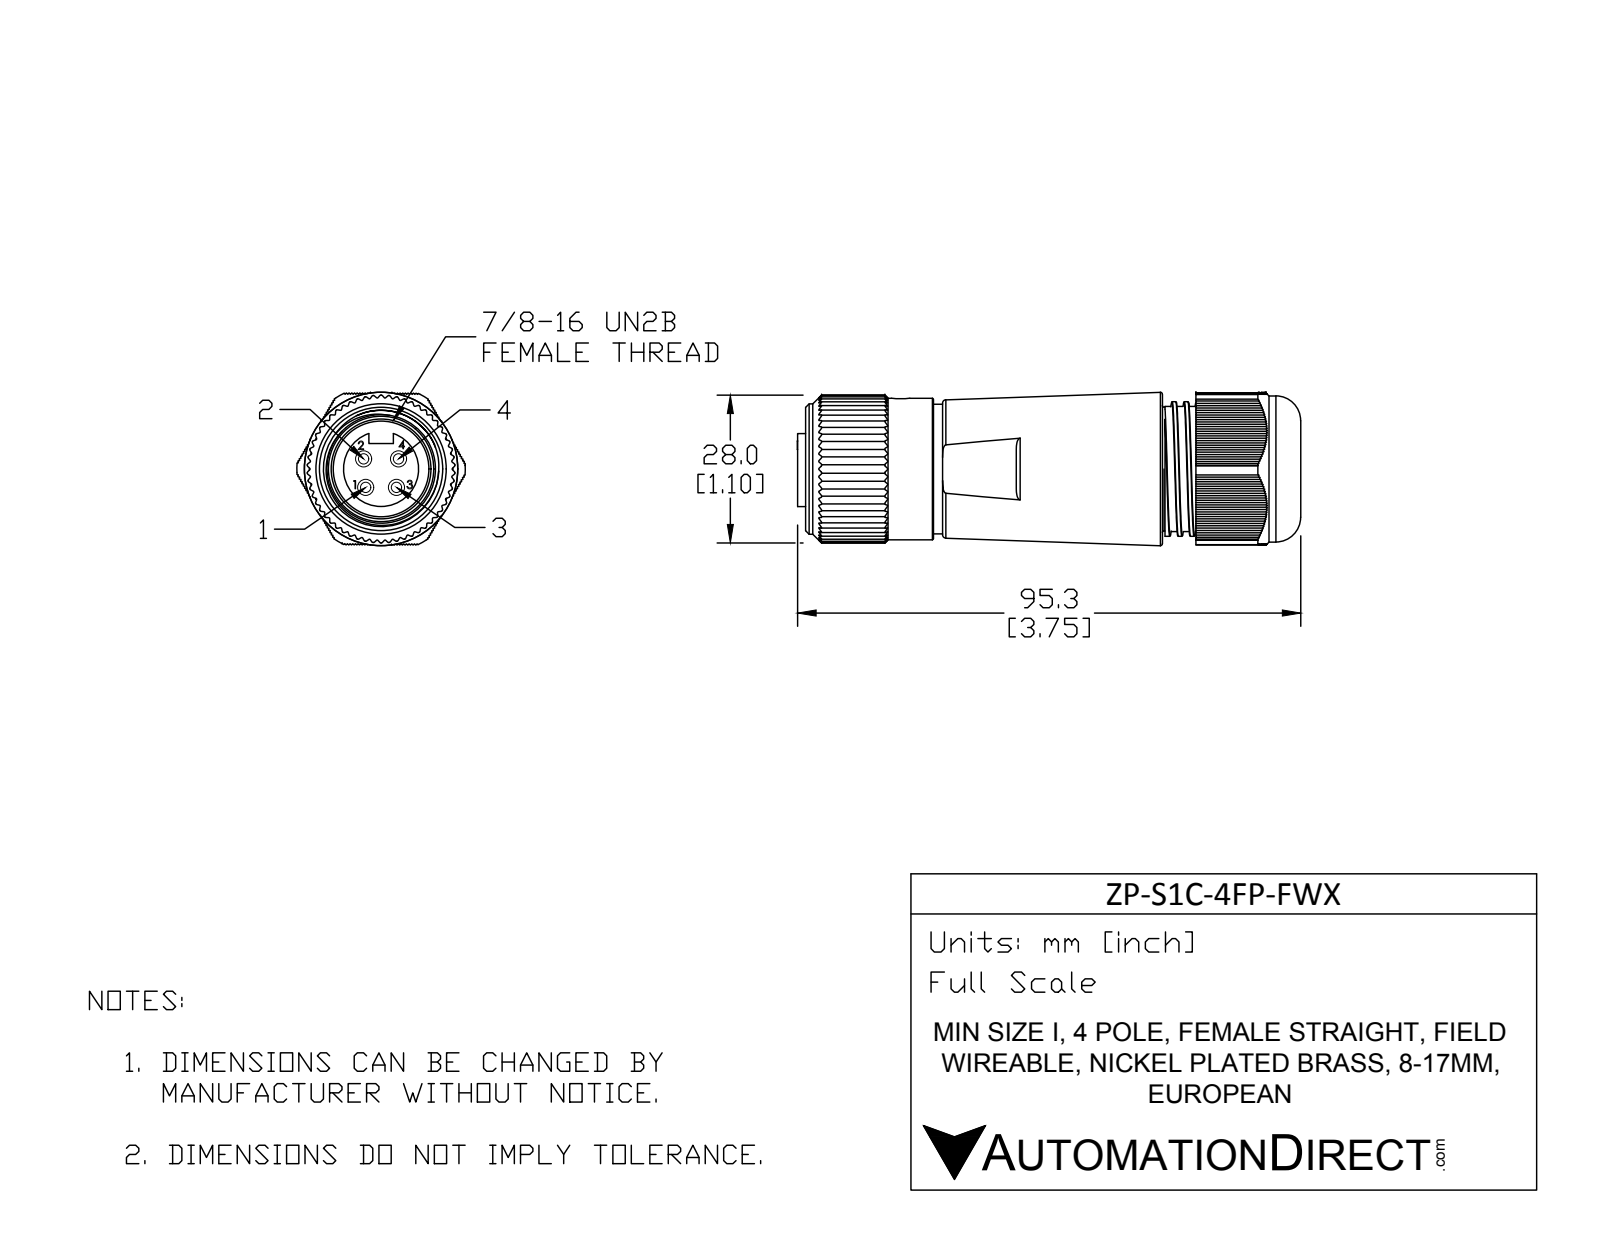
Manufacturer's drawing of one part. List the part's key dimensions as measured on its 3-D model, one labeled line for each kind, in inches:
Part name (STEP PRODUCT): ZP-S1C-4FP-FWX
STEP written by: SolidWorks 2015 (AUTOMOTIVE_DESIGN)
Units: inches
Bodies: 4 solids, 863 faces (509 planar, 303 cylindrical, 51 other)
Overall size (bounding box): 3.754 × 1.256 × 1.144
Volume: 3.034 in³ · Surface area: 25.44 in²
Round holes (diameter × count): ⌀0.12 ×4, ⌀0.138 ×1, ⌀0.68 ×1, ⌀0.81 ×1, ⌀0.849 ×1, ⌀0.953 ×1, ⌀1 ×1
Round bosses / shafts (diameter × count): ⌀1.09 ×1, ⌀1.055 ×1, ⌀1.004 ×1, ⌀0.972 ×1, ⌀0.967 ×1, ⌀0.714 ×1, ⌀0.56 ×1
Partial cylindrical surfaces — rounded edges, fillets, slot ends (radius × count): R0.01 ×165, R0.551 ×1, R0.628 ×1
Main face-to-face distances: 2.702, 0.042, 0.014, 0.028, 0.25, 2.722, 0.056, 0.083, 0.07, 0.346
Hole centre spacings: 0.15, 0.179, 0.212, 0.324, 0.23, 0.26
